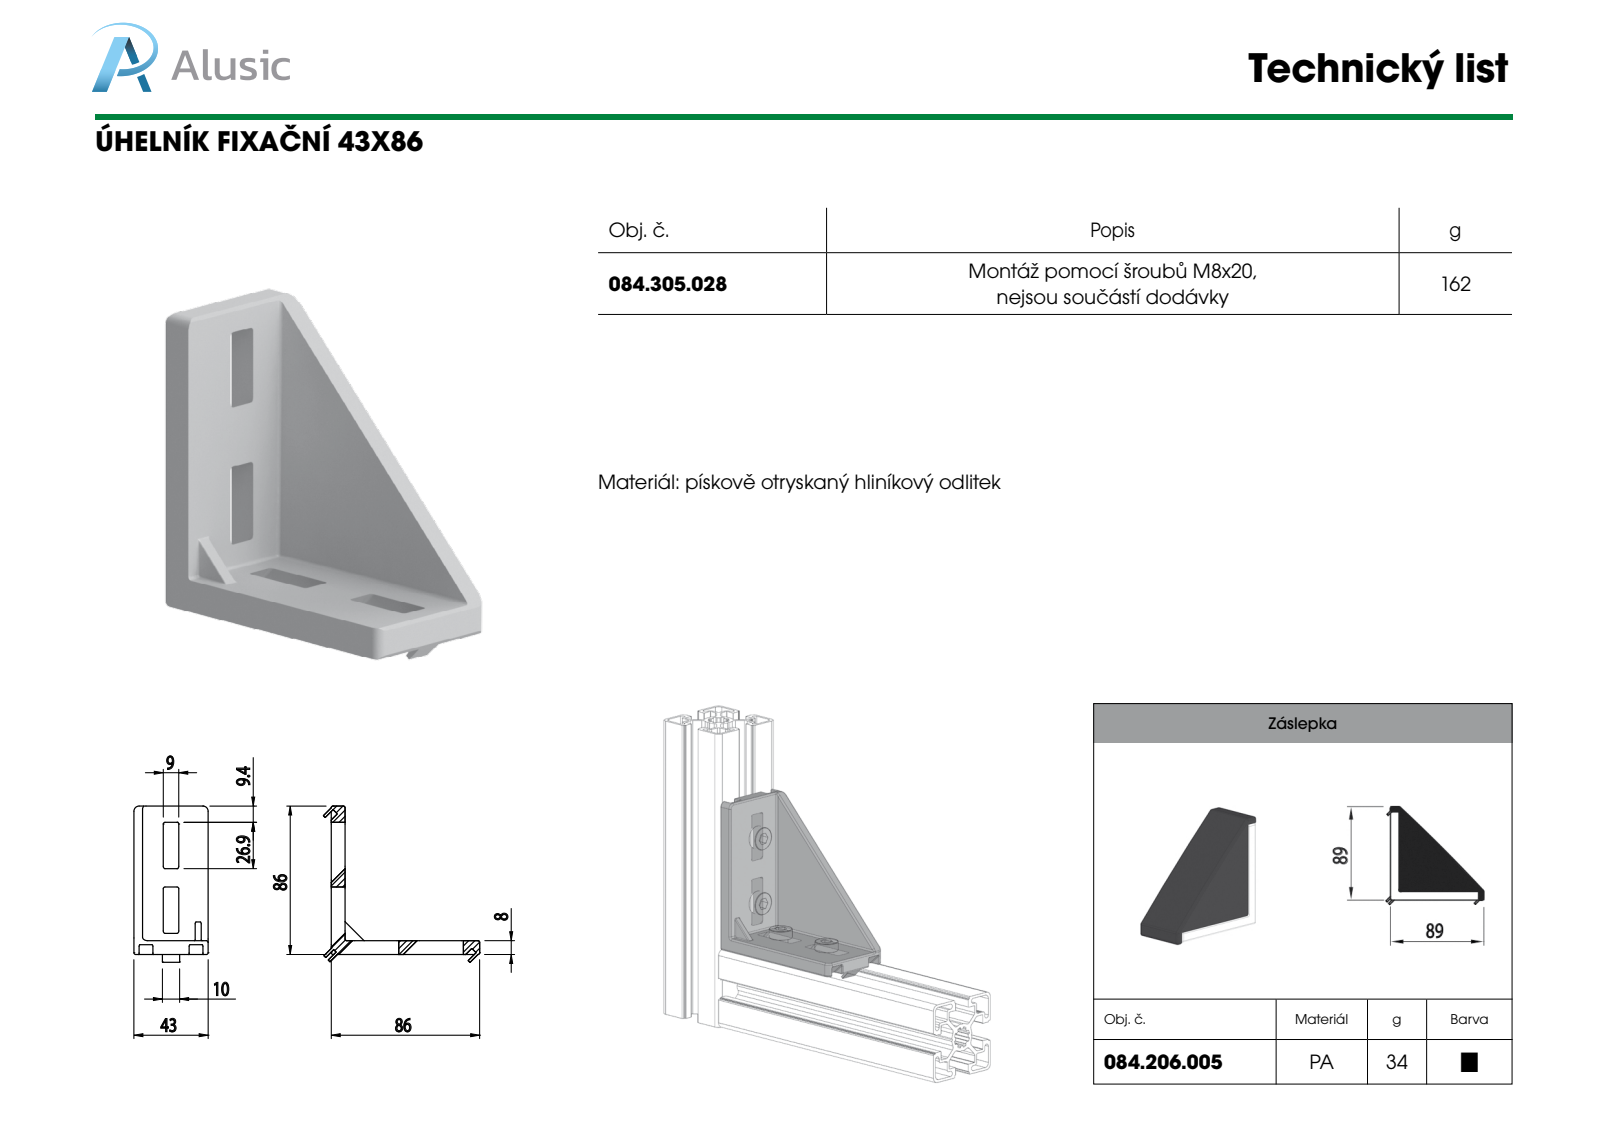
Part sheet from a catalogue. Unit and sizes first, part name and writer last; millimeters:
Units: millimetres
Overall size (bounding box): 89.98 × 89.98 × 43
Partial cylindrical surfaces — rounded edges, fillets, slot ends (radius × count): R1 ×5
Main face-to-face distances: 6, 4.5, 9.5, 5, 25.97, 12.98, 12.99, 76.5, 81, 86
Volume: 58 520 mm³ · Surface area: 27 511 mm²
Bodies: 1 solid, 116 faces (110 planar, 6 cylindrical, 0 other)
Part name (STEP PRODUCT): 084.305.028
STEP written by: SolidWorks 2011 (CONFIG_CONTROL_DESIGN)
